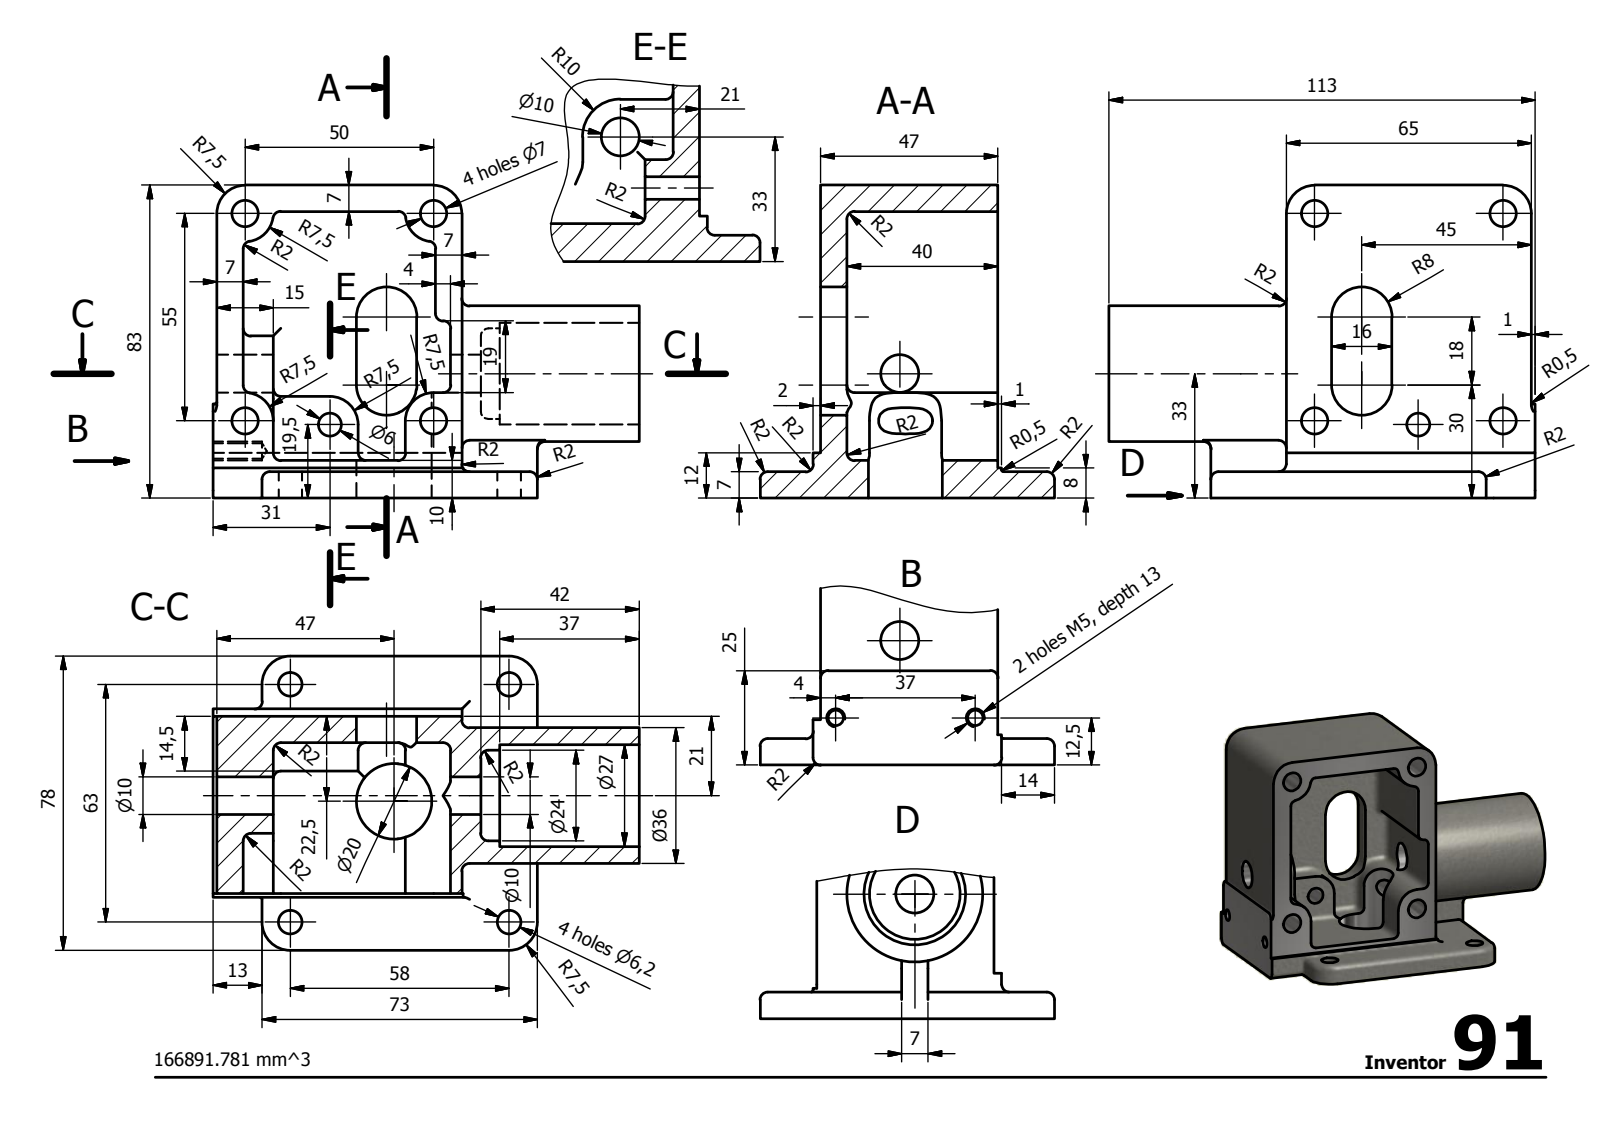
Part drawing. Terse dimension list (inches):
name: Piesa 091
written by: Autodesk Inventor 2014 (AUTOMOTIVE_DESIGN)
unit: in
bodies: 1 solid, 153 faces (42 planar, 77 cylindrical, 34 other)
size: 4.449 × 3.268 × 3.071
volume: 10.18 in³; area: 82.5 in²
holes: 4× ⌀0.244, 4× ⌀0.276, 2× ⌀0.163, 1× ⌀0.236, 1× ⌀0.394, 1× ⌀0.787, 1× ⌀0.945, 1× ⌀1.063
bosses: 1× ⌀1.417
rounds: 38× R0.079, 9× R0.295, 3× R0.02, 2× R0.315, 1× R0.394
face distances: 0.276, 2.992, 1.85, 3.268, 0.315, 2.598, 2.559, 2.283, 1.575, 0.118
hole spacings: 1.969, 2.165, 2.283, 2.48, 2.926, 3.371, 0.887, 1.048
